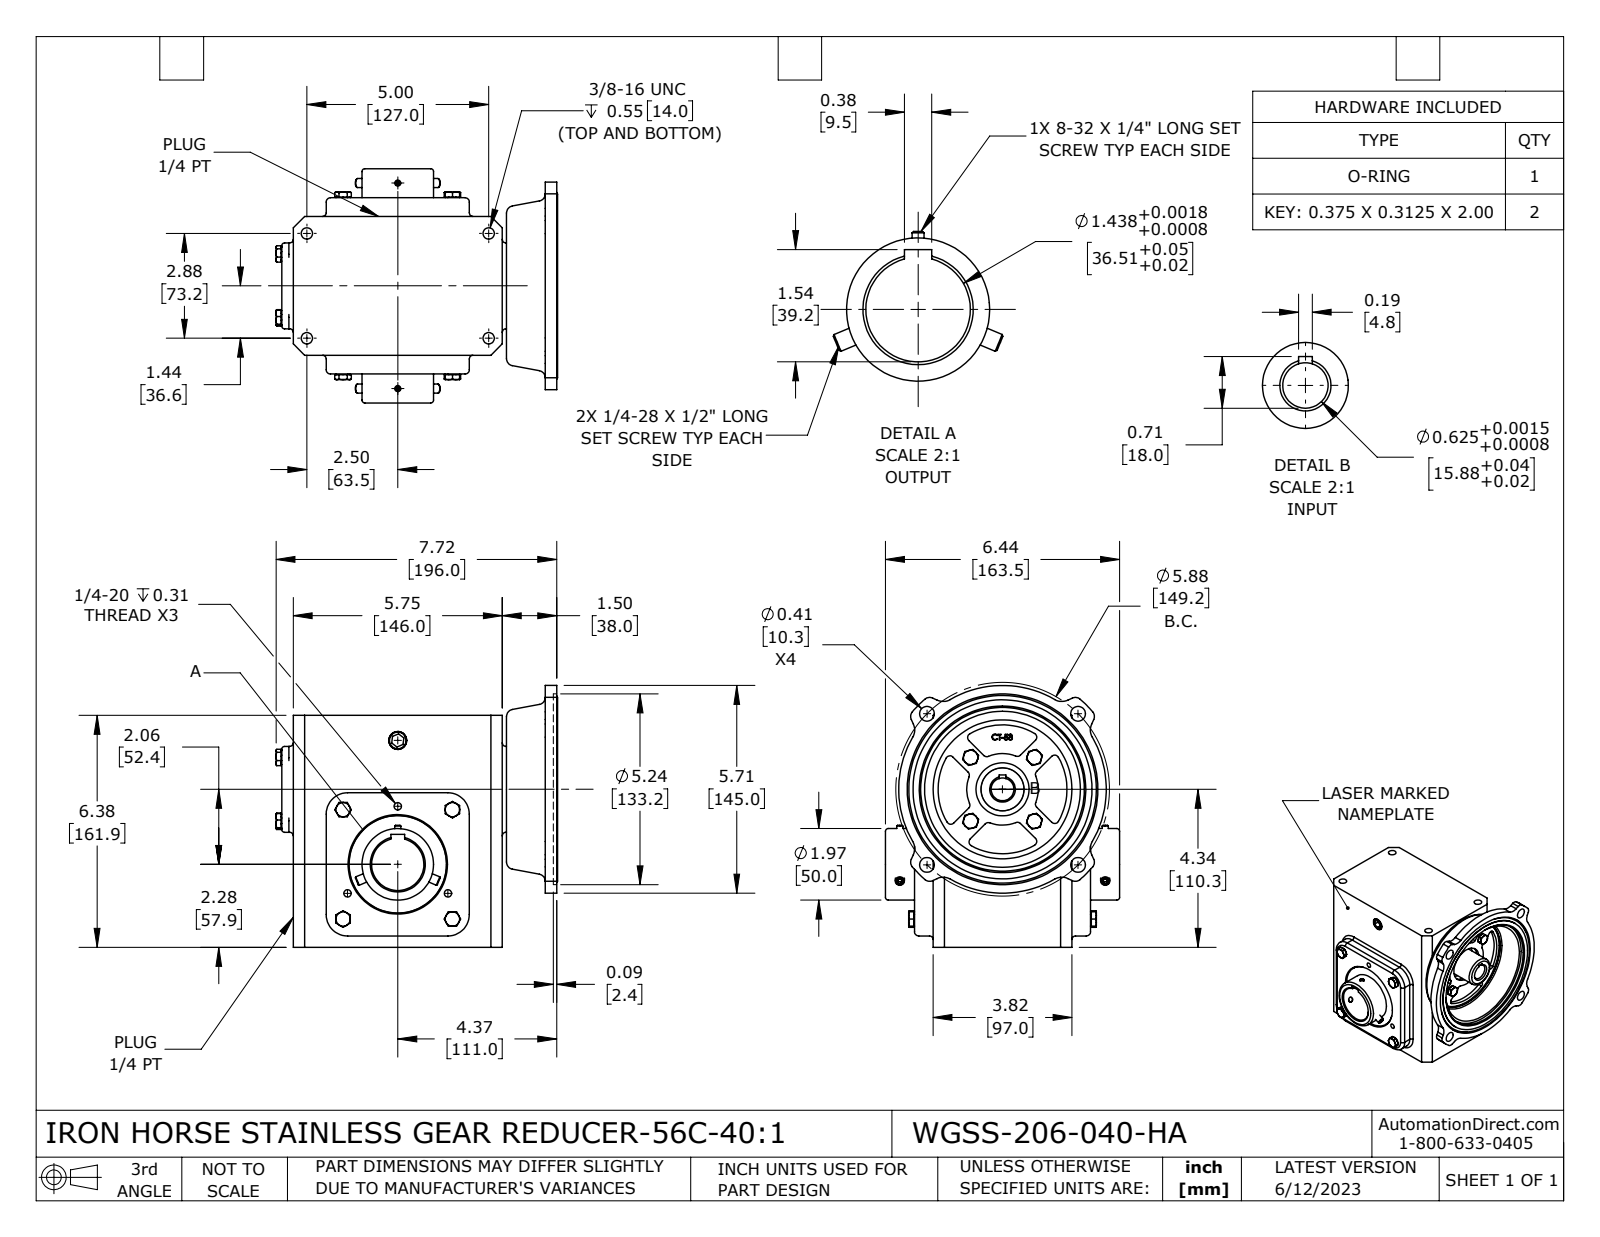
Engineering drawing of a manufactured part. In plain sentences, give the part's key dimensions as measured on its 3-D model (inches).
The part is named "WGSS-206-040-HA". Its 3-D file was written by "SolidWorks 2021 (CONFIG_CONTROL_DESIGN)". It is 7 solids with 895 faces: 396 planar, 235 cylindrical and 264 other. Overall it measures 7.74 by 7.197 by 6.437 inches. Its volume is 159.7 cubic inches and its surface area 323.7 square inches. Round holes: 4 of diameter 0.213, 4 of diameter 0.313, 4 of diameter 0.406, 3 of diameter 0.201, 2 of diameter 0.136, 1 of diameter 0.625, 1 of diameter 0.866, 1 of diameter 1.437, 1 of diameter 1.441, 1 of diameter 1.457, 1 of diameter 1.575, 1 of diameter 3.819. Round bosses or shafts: 8 of diameter 0.394, 4 of diameter 0.25, 2 of diameter 0.164, 1 of diameter 4.921, 1 of diameter 2.677, 1 of diameter 1.969, 1 of diameter 1.181. Partial cylindrical surfaces (rounded edges, fillets, slot ends): 24 of radius 0.118, 16 of radius 0.098, 12 of radius 0.394, 8 of radius 0.197, 4 of radius 0.079, 4 of radius 0.315, 4 of radius 0.591, 1 of radius 0.984. The main face-to-face distances are 6.375, 3.819, 0.512, 4.331, 5.748, 0.118, 0.315, 7.244, 4.843, 0.157. The hole center spacings are 2.858, 2.937, 4.154, 4.944, 1.594, 5.65, 2.762, 2.88.
